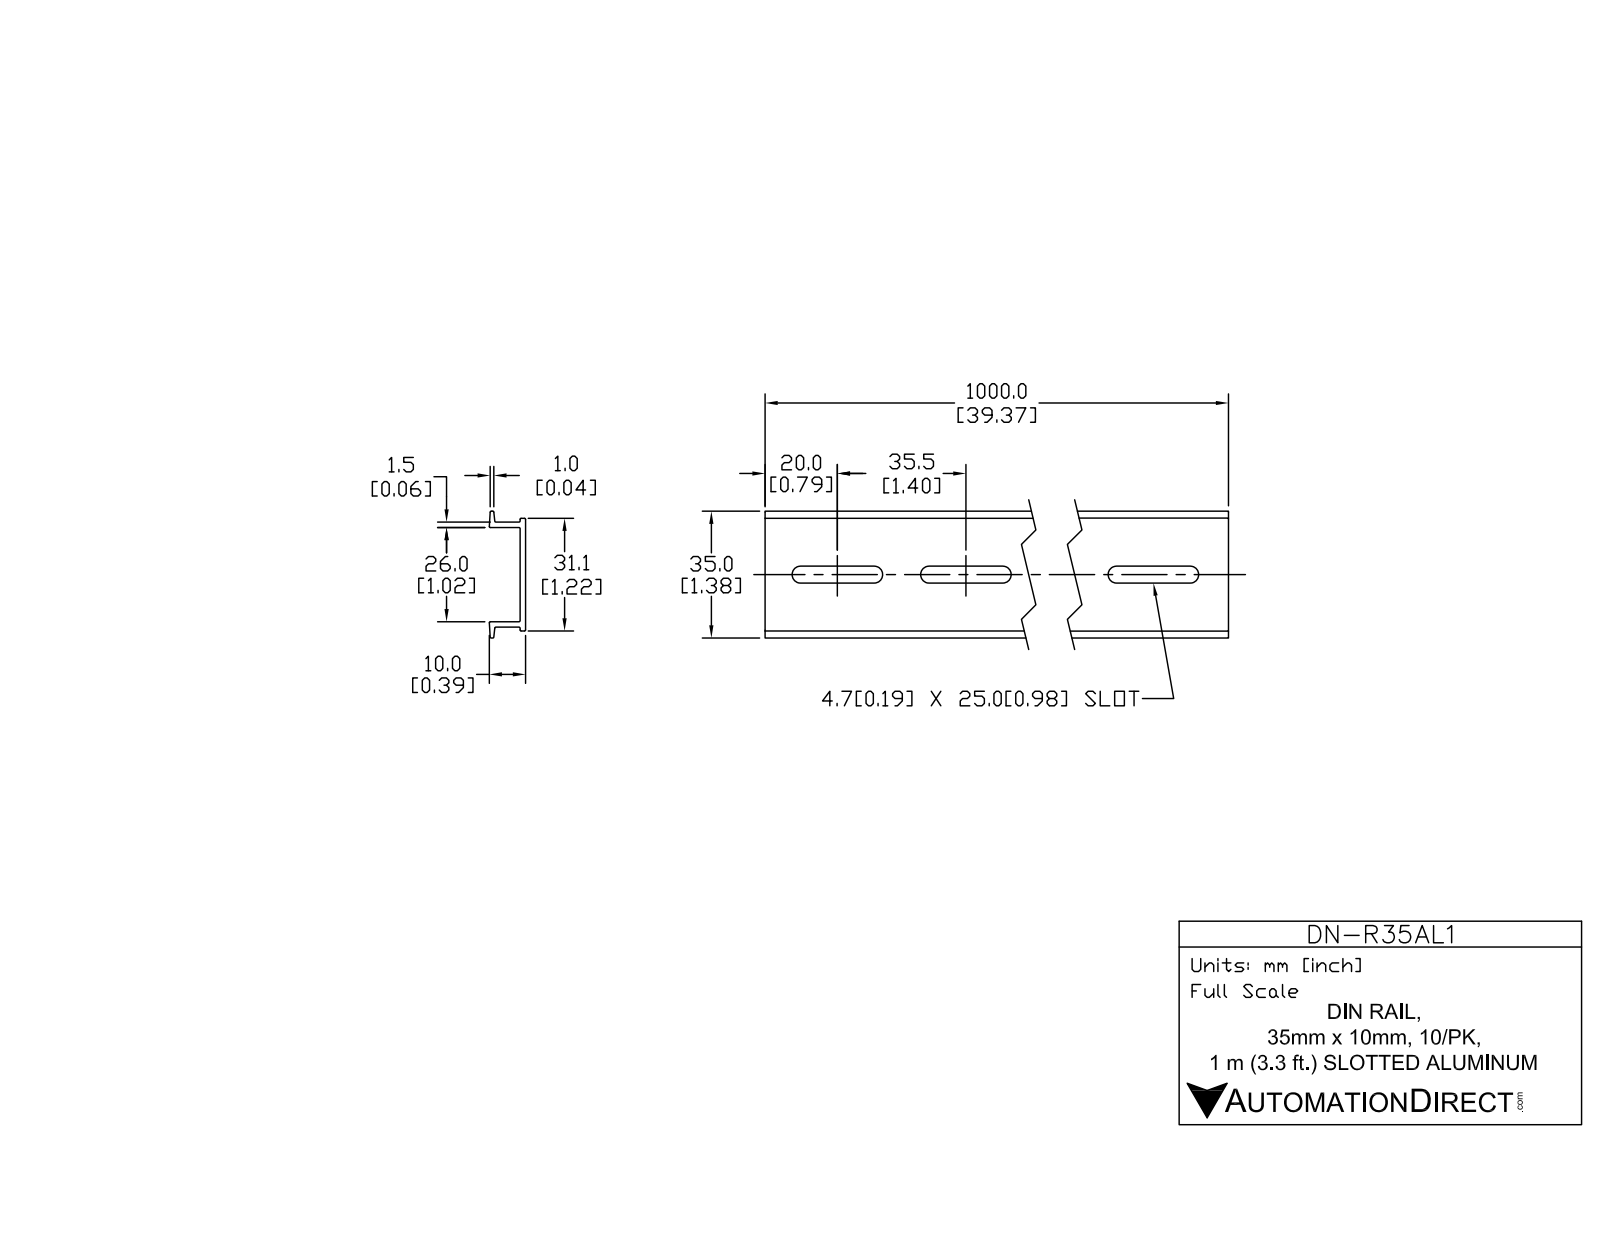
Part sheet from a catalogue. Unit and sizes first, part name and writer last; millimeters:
Units: millimetres
Overall size (bounding box): 1000 × 35 × 10
Partial cylindrical surfaces — rounded edges, fillets, slot ends (radius × count): R2.35 ×56, R0.27 ×16
Main face-to-face distances: 1.5, 27.5, 8.5, 26, 10, 29, 7, 1.1, 2.6, 28.6
Volume: 76 502 mm³ · Surface area: 105 733 mm²
Bodies: 1 solid, 146 faces (74 planar, 72 cylindrical, 0 other)
Part name (STEP PRODUCT): DN-R35SAL1
STEP written by: SolidWorks 2011 (AUTOMOTIVE_DESIGN)
